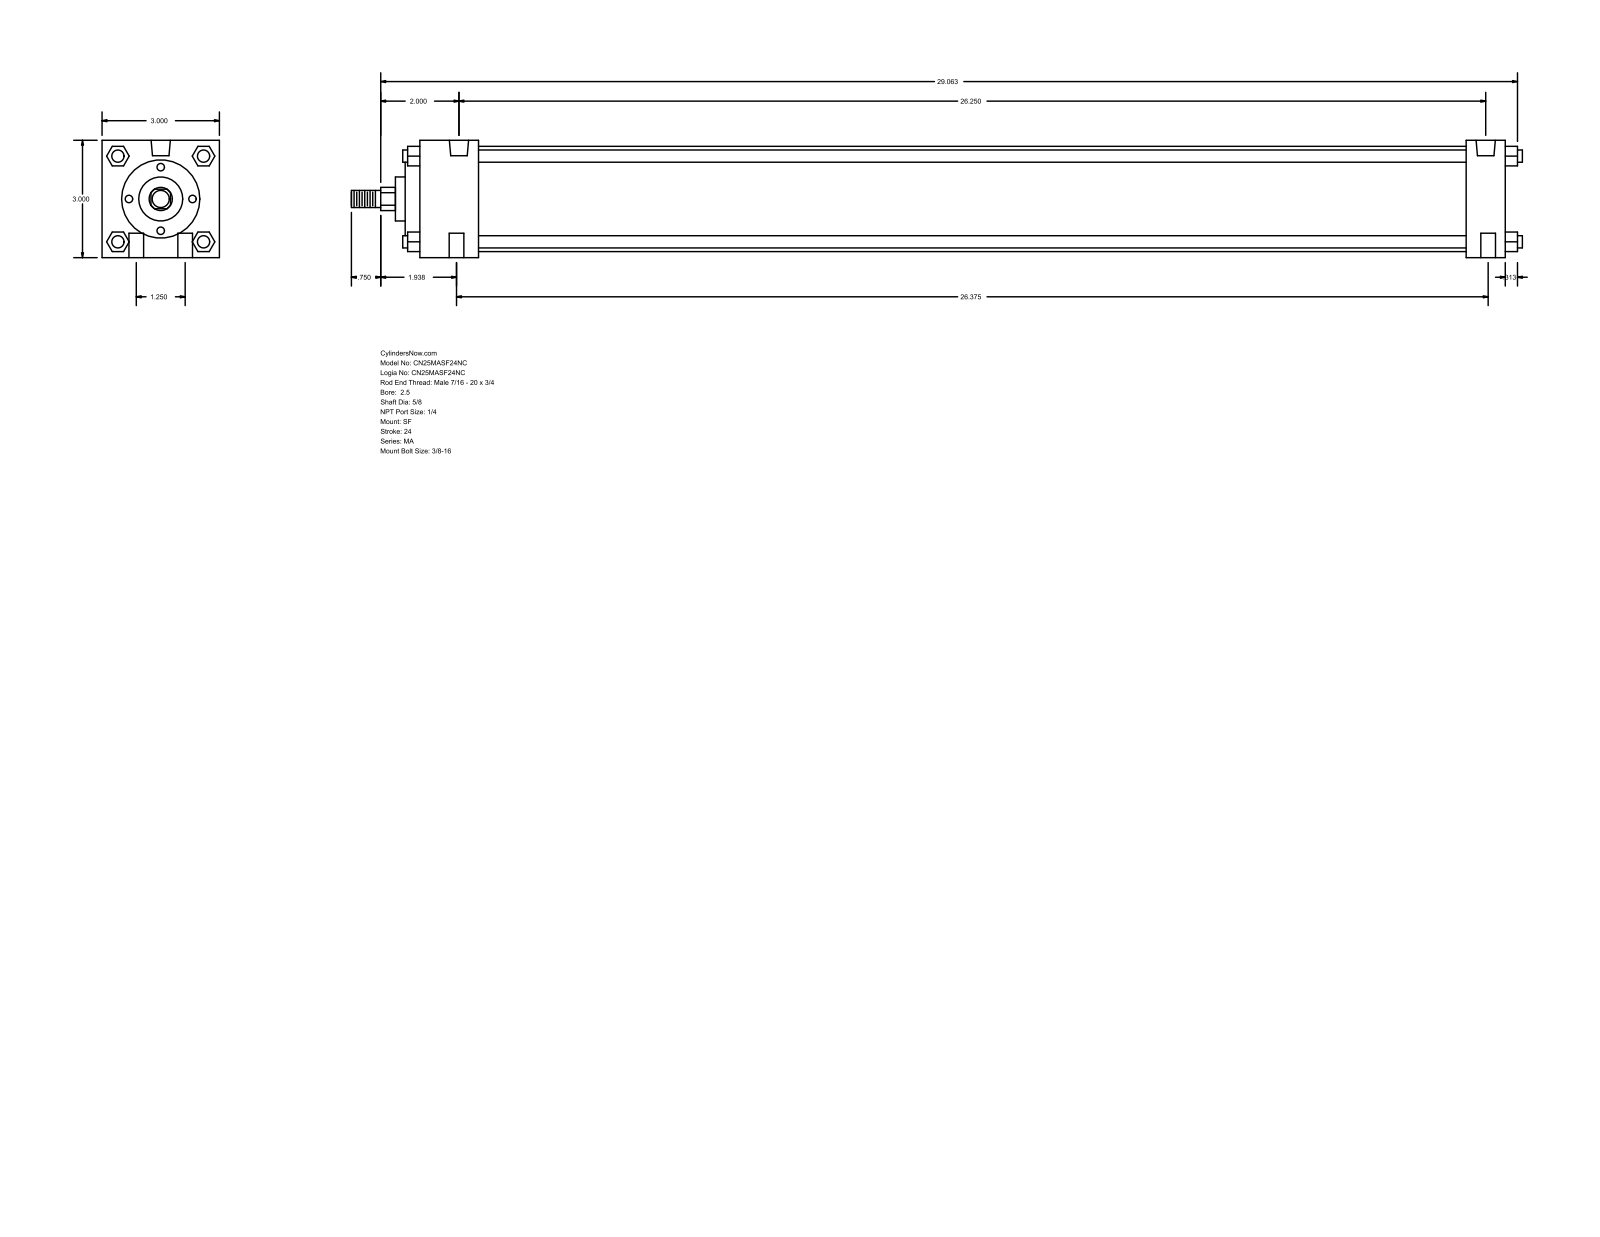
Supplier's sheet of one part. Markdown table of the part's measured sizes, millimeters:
| quantity | value |
| --- | --- |
| part name | MA_SF__0250_0.625 |
| STEP written by | GSSL Pune (CONFIG_CONTROL_DESIGN) |
| units | millimeters |
| bodies | 0 solids, 126 faces (95 planar, 31 cylindrical, 0 other) |
| overall size | 760.41 × 76.2 × 76.2 |
| round holes (diameter × count) | 9.53 × 4, 7.94 × 2, 12.49 × 2 |
| round bosses / shafts (diameter × count) | 7.94 × 4, 68.33 × 1, 50.8 × 1, 28.57 × 1, 15.88 × 1, 11.11 × 1 |
| partial cylindrical surfaces (radius × count) | 7.54 × 1 |
| main face-to-face distances | 76.2, 704.85, 25.4, 679.45, 38.1, 641.35, 666.75, 12.7, 9.52, 47.62 |
| hole center spacings | 15.96, 668.53, 31.76, 666.75, 669.93, 670.68 |
